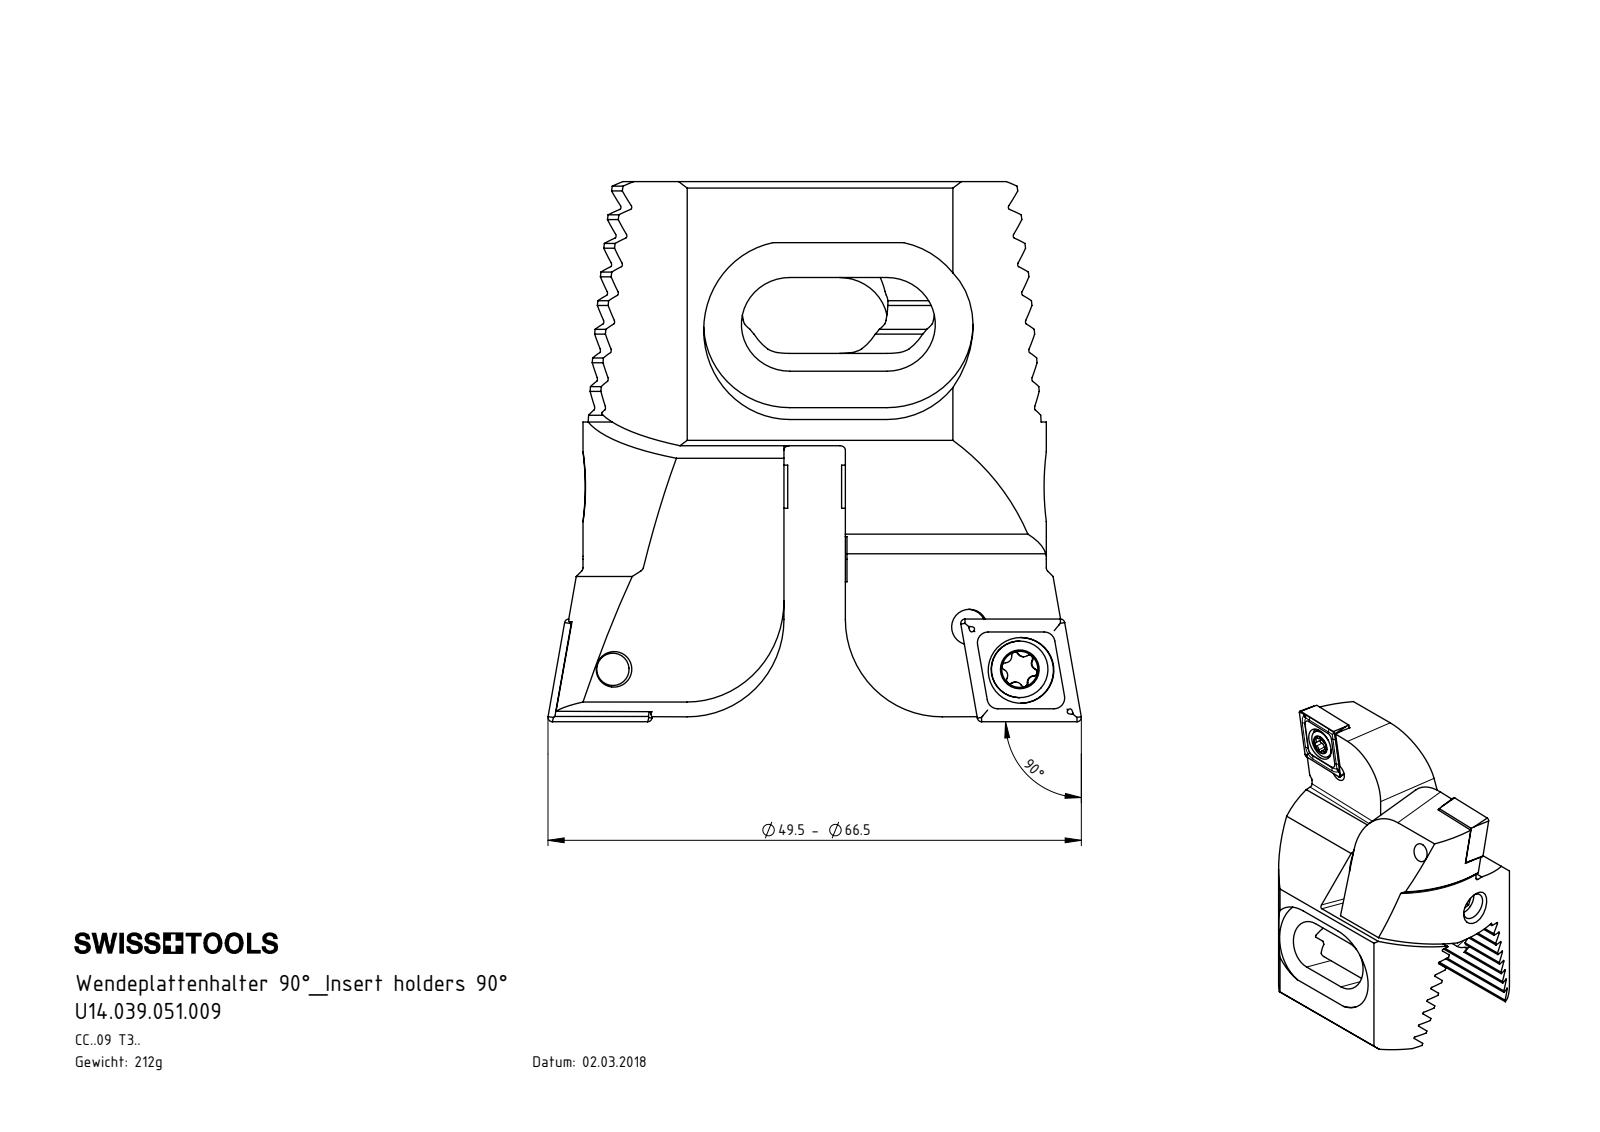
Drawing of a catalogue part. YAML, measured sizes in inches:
part_name: "Z42-ER3.001.016; CCMT09T304; Z42.WCB.B11.028; Z42-WCB.001.028_A (+1 more)"
step_written_by: "SolidWorks 2017 (AUTOMOTIVE_DESIGN)"
units: inches
bodies: {solids: 8, faces: 374, planar: 184, cylindrical: 98, other: 92}
overall_size: [1.972, 1.949, 1.346]
volume: 1.646
surface_area: 20.87
round_holes:
  - {diameter: 0.13, count: 4}
  - {diameter: 0.039, count: 2}
  - {diameter: 0.173, count: 2}
  - {diameter: 0.24, count: 2}
  - {diameter: 0.197, count: 1}
round_bosses_or_shafts:
  - {diameter: 0.157, count: 3}
  - {diameter: 0.207, count: 2}
  - {diameter: 0.236, count: 1}
partial_cylinders:
  - {radius: 0.008, count: 16}
  - {radius: 0.013, count: 12}
  - {radius: 0.023, count: 12}
  - {radius: 0.039, count: 8}
  - {radius: 0.02, count: 4}
  - {radius: 0.177, count: 4}
  - {radius: 0.315, count: 4}
  - {radius: 0.354, count: 2}
face_to_face_distances: [0.094, 0.187, 0.469, 0.375, 0.563, 0.281, 0.196, 0.281, 0.041, 0.656]
hole_center_spacings: [0.24, 0.512, 1.322, 0.246, 0.246, 0.989, 1.13, 1.327]
